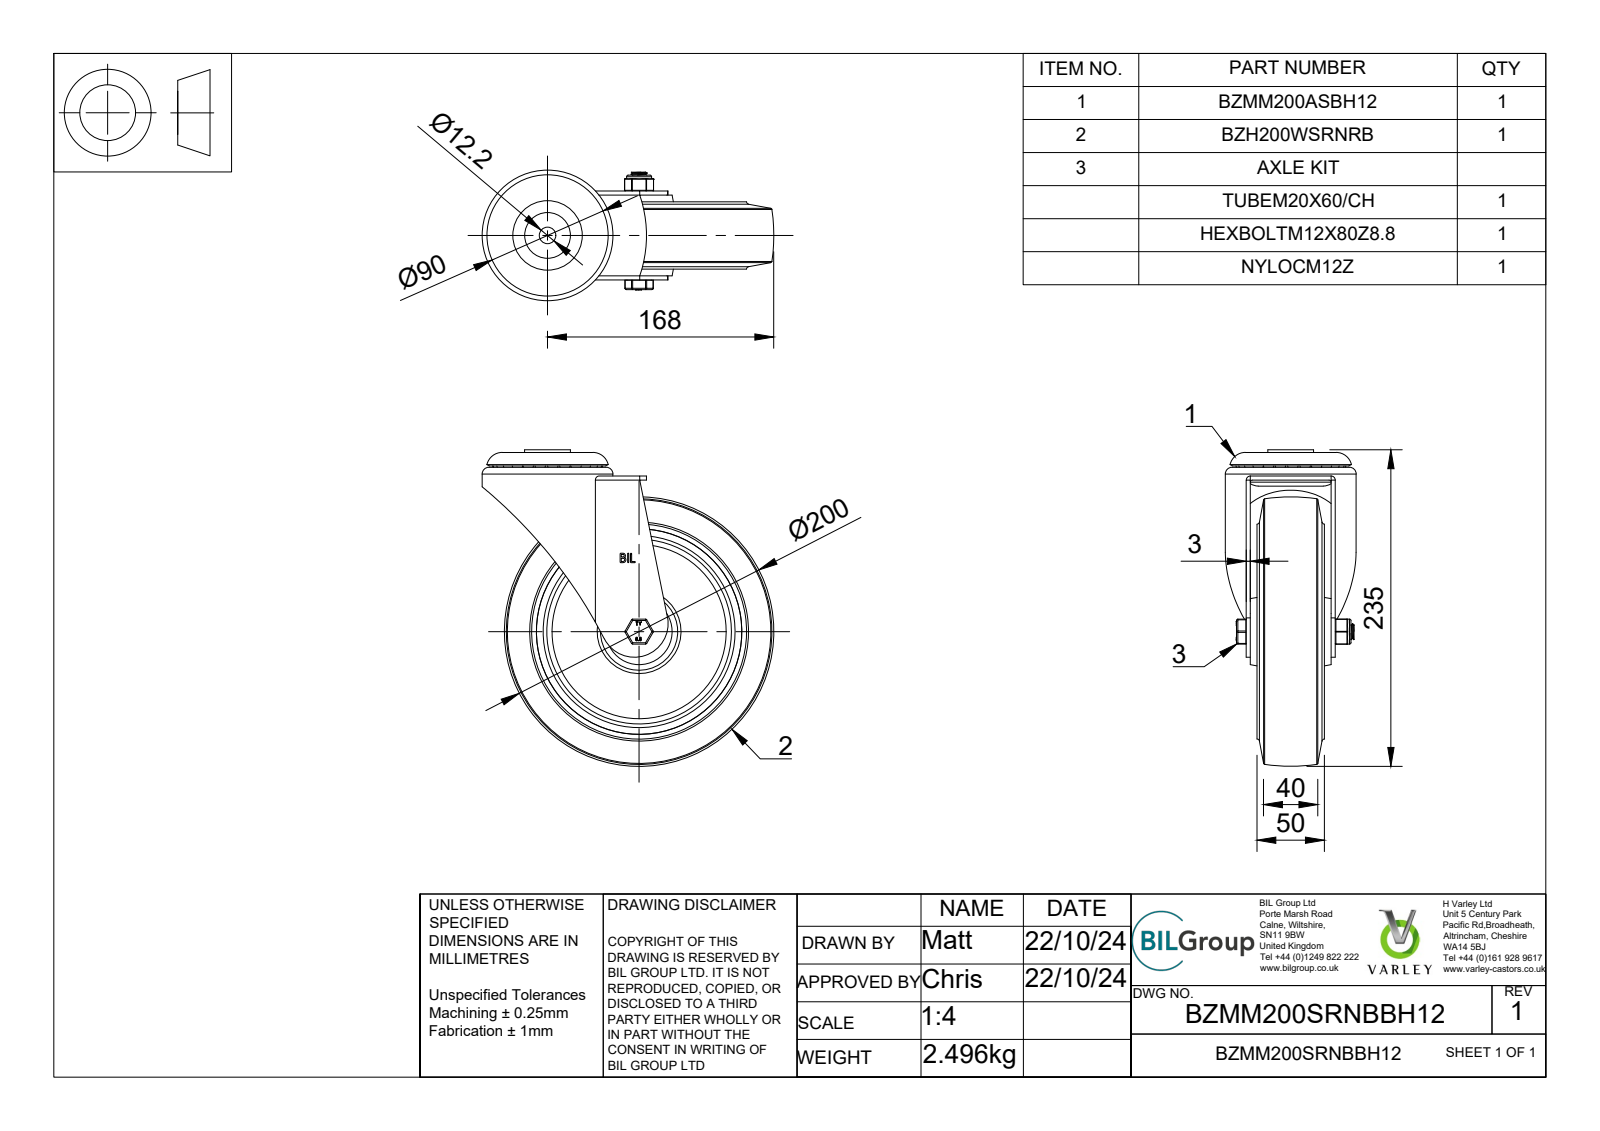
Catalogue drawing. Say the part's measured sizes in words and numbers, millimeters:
The part is named "BZMM200SRNBBH12 v3; BZMM200ASBH12 v1; ZINC PLATED, PRESSED STEEL HEAD; ZINC PLATED, PRESSED STEEL HEAD Geometry (+6 more)". Its 3-D file was written by "Autodesk Translation Framework v13.20.0.188 (AUTOMOTIVE_DESIGN)". It is 62 solids with 451 faces: 176 planar, 129 cylindrical and 146 other. Overall it measures 235 by 216.5 by 97 millimeters. Its volume is 1 134 000 cubic millimeters and its surface area 282 440 square millimeters. Round holes: 1 of diameter 12, 1 of diameter 12.2, 1 of diameter 12.3, 1 of diameter 12.5, 1 of diameter 14, 1 of diameter 20, 1 of diameter 30.2, 1 of diameter 51, 1 of diameter 58, 1 of diameter 91, 1 of diameter 152.5. Round bosses or shafts: 8 of diameter 5, 1 of diameter 97, 1 of diameter 63, 1 of diameter 39, 1 of diameter 34, 1 of diameter 30, 1 of diameter 24, 1 of diameter 19.9. Partial cylindrical surfaces (rounded edges, fillets, slot ends): 18 of radius 0.5, 12 of radius 1, 4 of radius 1.5, 2 of radius 3, 1 of radius 13.5, 1 of radius 25, 1 of radius 92.5, 1 of radius 358.69. The main face-to-face distances are 25, 35, 3, 63, 28, 38, 10, 5, 8, 20.
